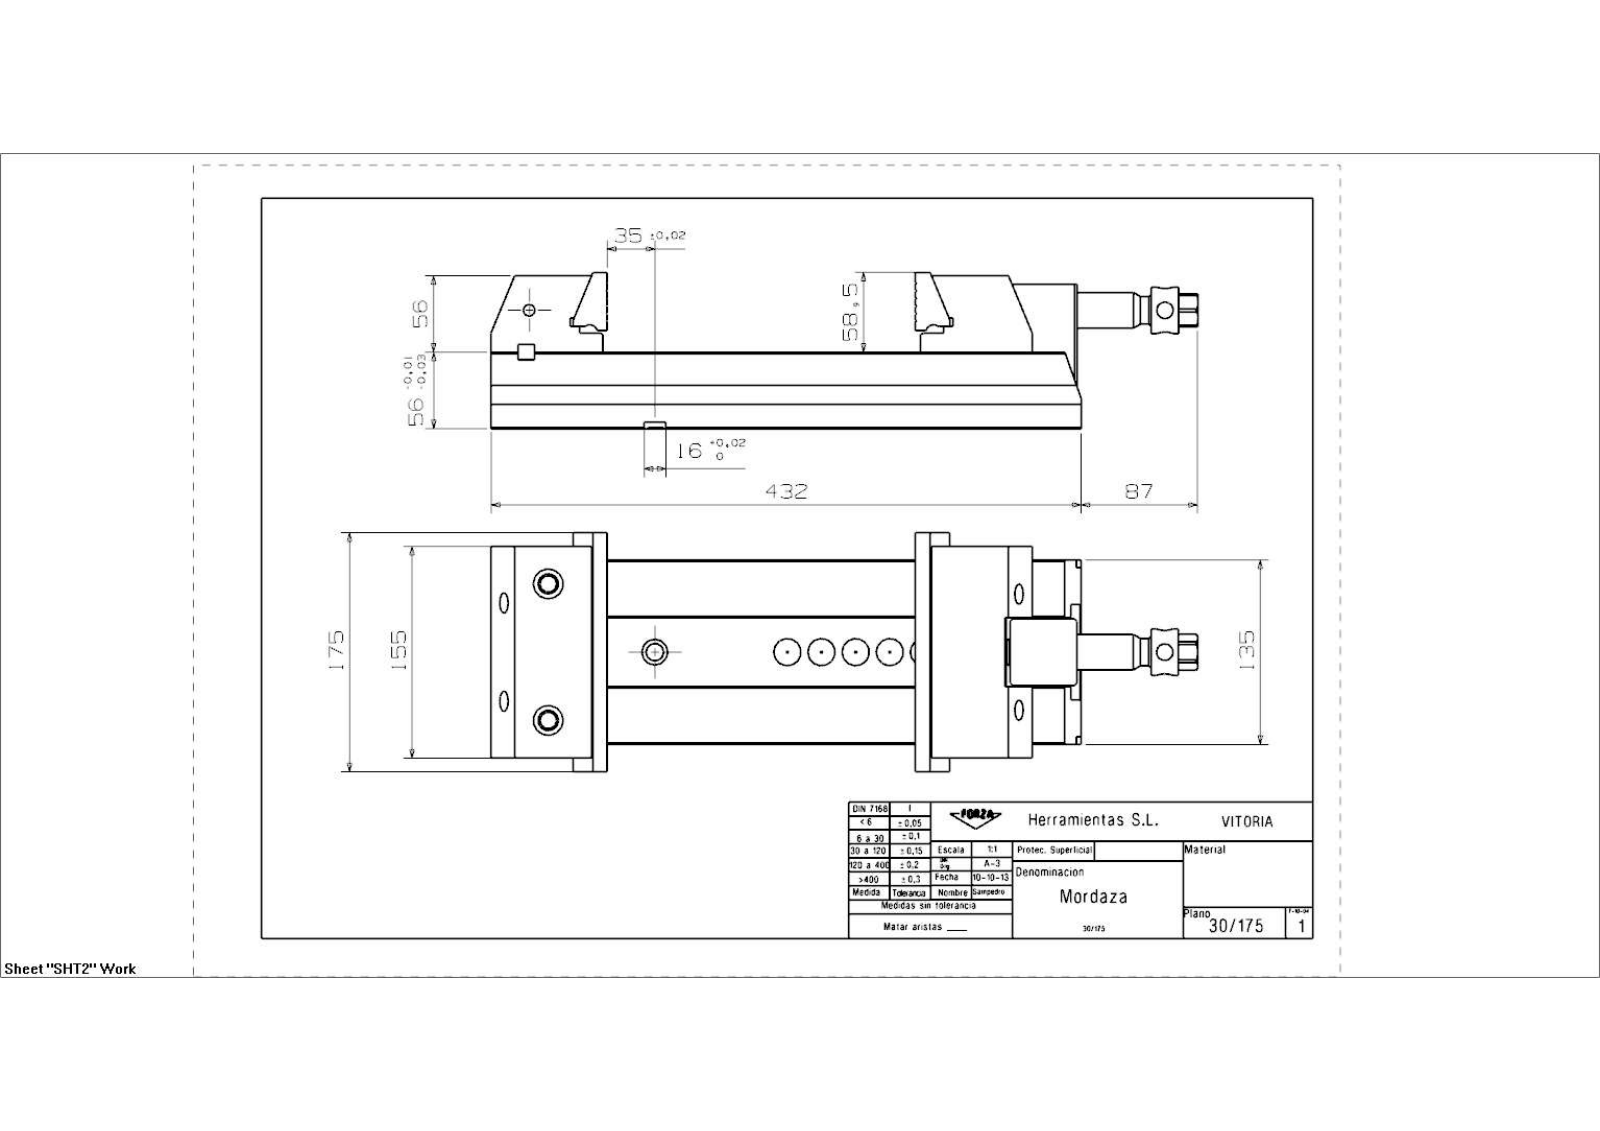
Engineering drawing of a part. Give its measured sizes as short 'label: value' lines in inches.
name: 30_175_Mordaza
written by: SIEMENS PLM Software NX 7.5 (CONFIG_CONTROL_DESIGN)
unit: in
bodies: 12 solids, 459 faces (303 planar, 95 cylindrical, 61 other)
size: 20.363 × 6.89 × 4.508
volume: 233.4 in³; area: 760 in²
holes: 6× ⌀0.512, 6× ⌀0.591, 6× ⌀0.748, 5× ⌀0.204, 4× ⌀0.394, 4× ⌀0.417, 3× ⌀0.346, 2× ⌀0.275, 2× ⌀0.335, 2× ⌀0.472, 2× ⌀0.487, 2× ⌀0.866
bosses: 1× ⌀1.339, 1× ⌀1.331, 1× ⌀1.024, 1× ⌀0.787, 1× ⌀0.65
rounds: 4× R0.315, 4× R0.787, 2× R0.063, 2× R0.236, 2× R0.276, 1× R0.157, 1× R0.354, 1× R0.413
face distances: 2.205, 1.252, 0.953, 2.161, 5.315, 0.394, 4.411, 3.459, 2.207, 0.043
hole spacings: 0.256, 2.835, 3.091, 4.176, 1.093, 1.144, 1.181, 1.347
